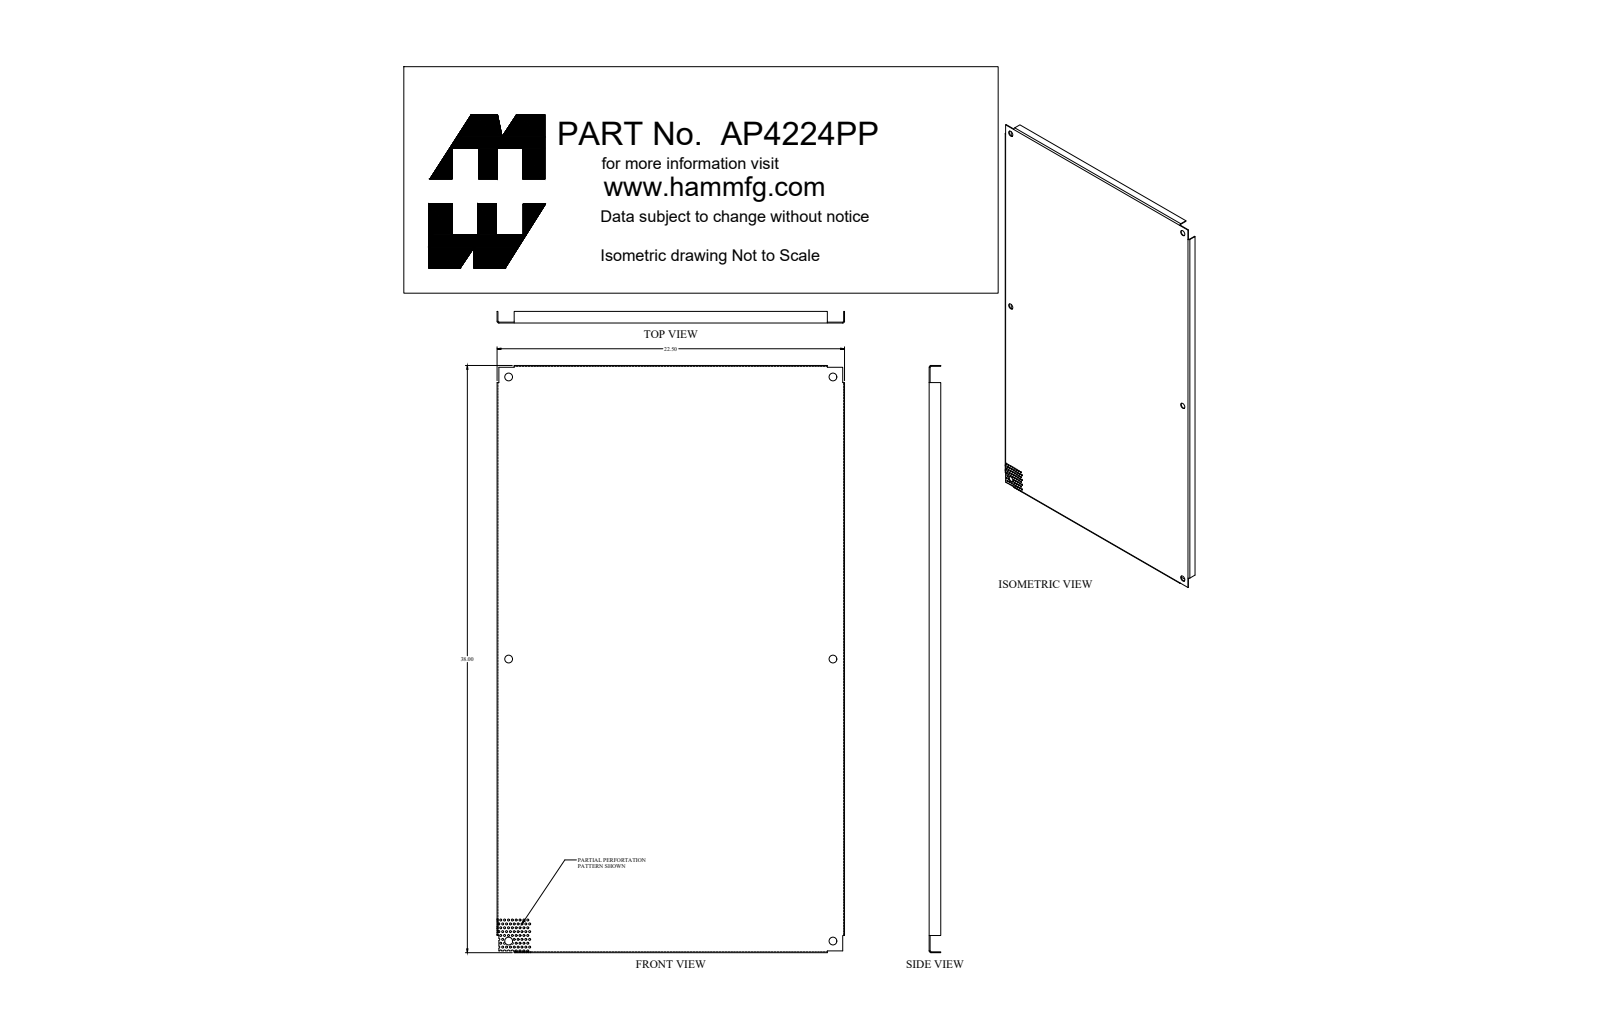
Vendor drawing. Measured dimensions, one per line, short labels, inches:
name: AP4224PP_Default
written by: SolidWorks 2019 (CONFIG_CONTROL_DESIGN)
unit: in
bodies: 1 solid, 253 faces (43 planar, 202 cylindrical, 8 other)
size: 38 × 22.5 × 0.75
volume: 52.81 in³; area: 1 863 in²
holes: 76× ⌀0.125, 6× ⌀0.5
rounds: 13× R0.063, 8× R0.062, 4× R0.029, 4× R0.086
face distances: 0.057, 22.443, 37.943, 22.386, 22.5, 37.886, 38, 0.75, 0.693, 0.102
hole spacings: 0.28, 0.5, 0.25, 0.559, 0.451, 0.76, 0.673, 0.75
